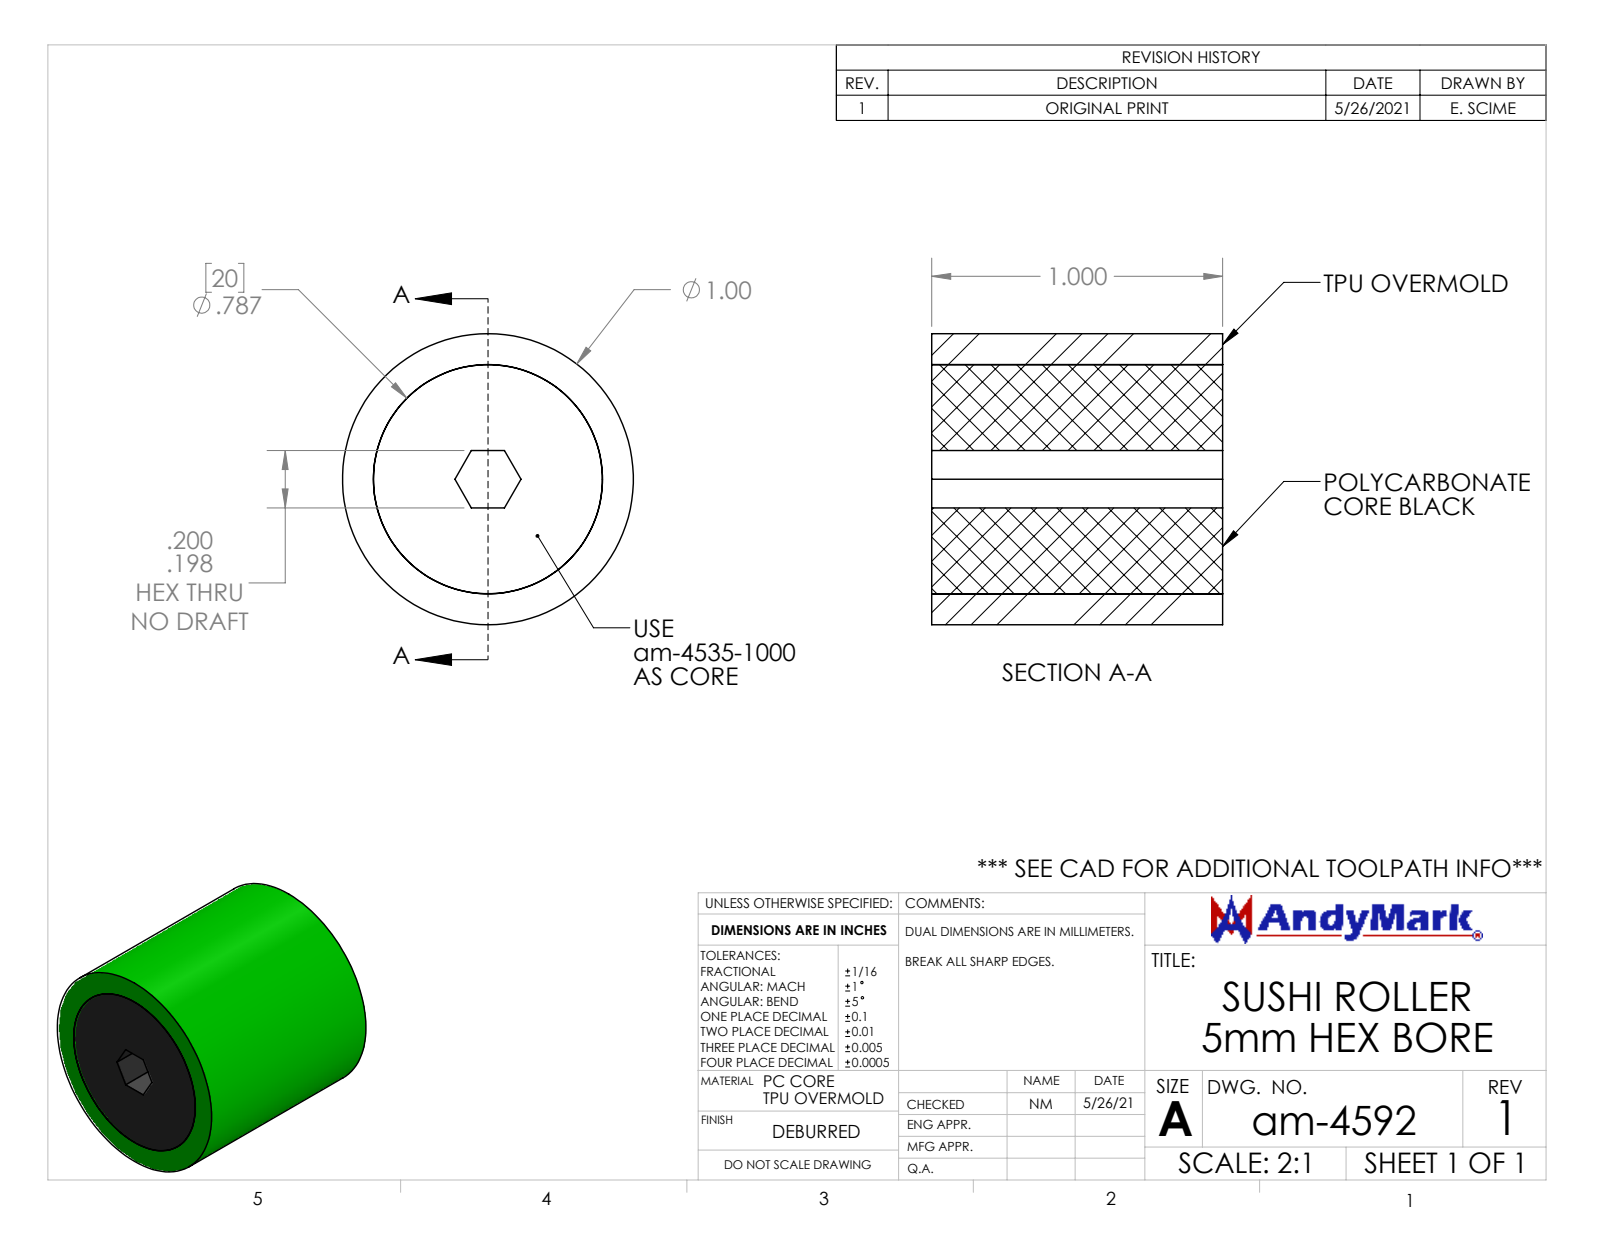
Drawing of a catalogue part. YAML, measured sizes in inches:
part_name: "am-4592 Sushi Roller 5mm Hex Bore"
step_written_by: "SolidWorks 2019 (AUTOMOTIVE_DESIGN)"
units: inches
bodies: {solids: 2, faces: 16, planar: 10, cylindrical: 6, other: 0}
overall_size: [1, 1, 1]
volume: 0.752
surface_area: 10.27
round_holes:
  - {diameter: 0.787, count: 1}
round_bosses_or_shafts:
  - {diameter: 1, count: 1}
face_to_face_distances: [1, 0.197]
